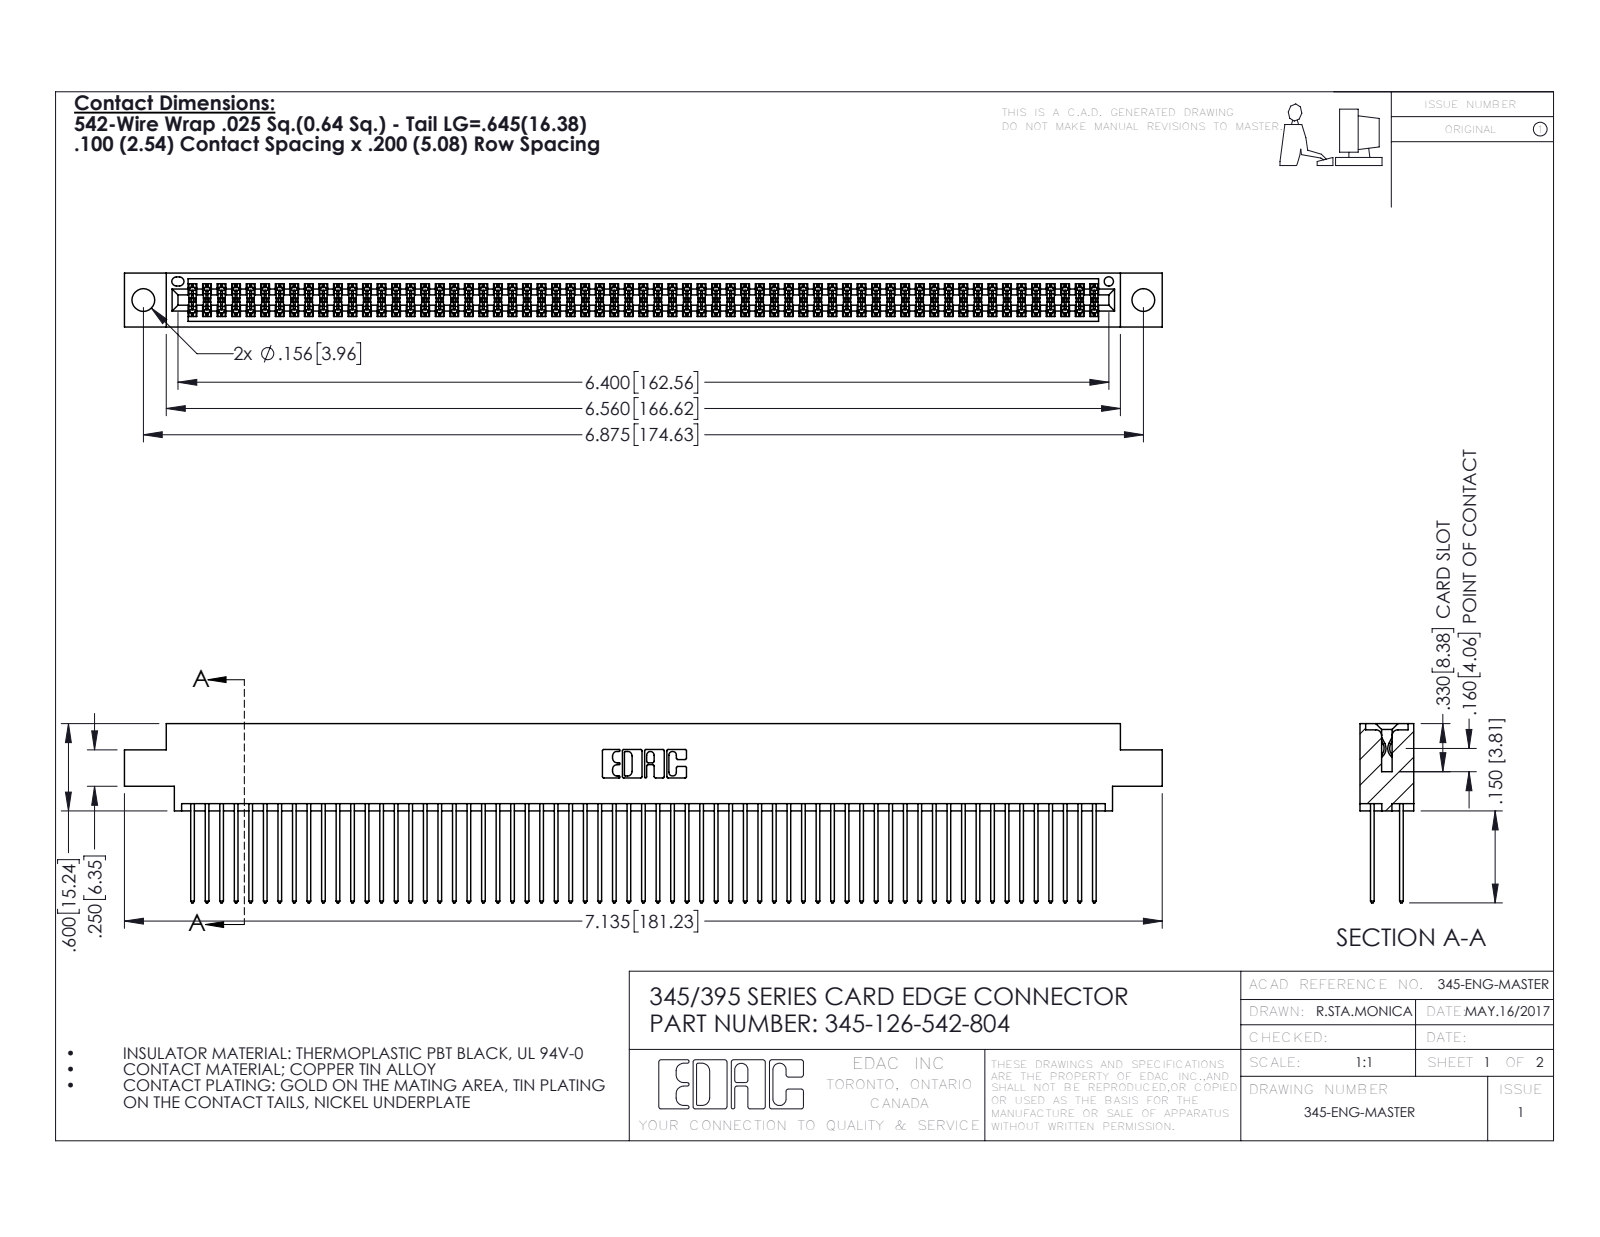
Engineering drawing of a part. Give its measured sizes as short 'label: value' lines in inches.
name: 345-126-542-804; 345 Part_0.170 Offset - 0.156 Dia-TI; 345-292-001_345-293-142
written by: SolidWorks 2020 (CONFIG_CONTROL_DESIGN)
unit: in
bodies: 127 solids, 6444 faces (4256 planar, 2188 cylindrical, 0 other)
size: 7.135 × 1.232 × 0.37
volume: 1.109 in³; area: 46.5 in²
holes: 2× ⌀0.156, 1× ⌀0.064
rounds: 189× R0.006, 126× R0.01, 22× R0.01, 6× R0.007, 6× R0.031, 3× R0.026, 2× R0.014, 2× R0.019
face distances: 0.072, 0.298, 0.2, 0.098, 0.272, 0.025, 0.37, 0.225, 0.175, 0.149
hole spacings: 0.27, 6.639, 6.875
